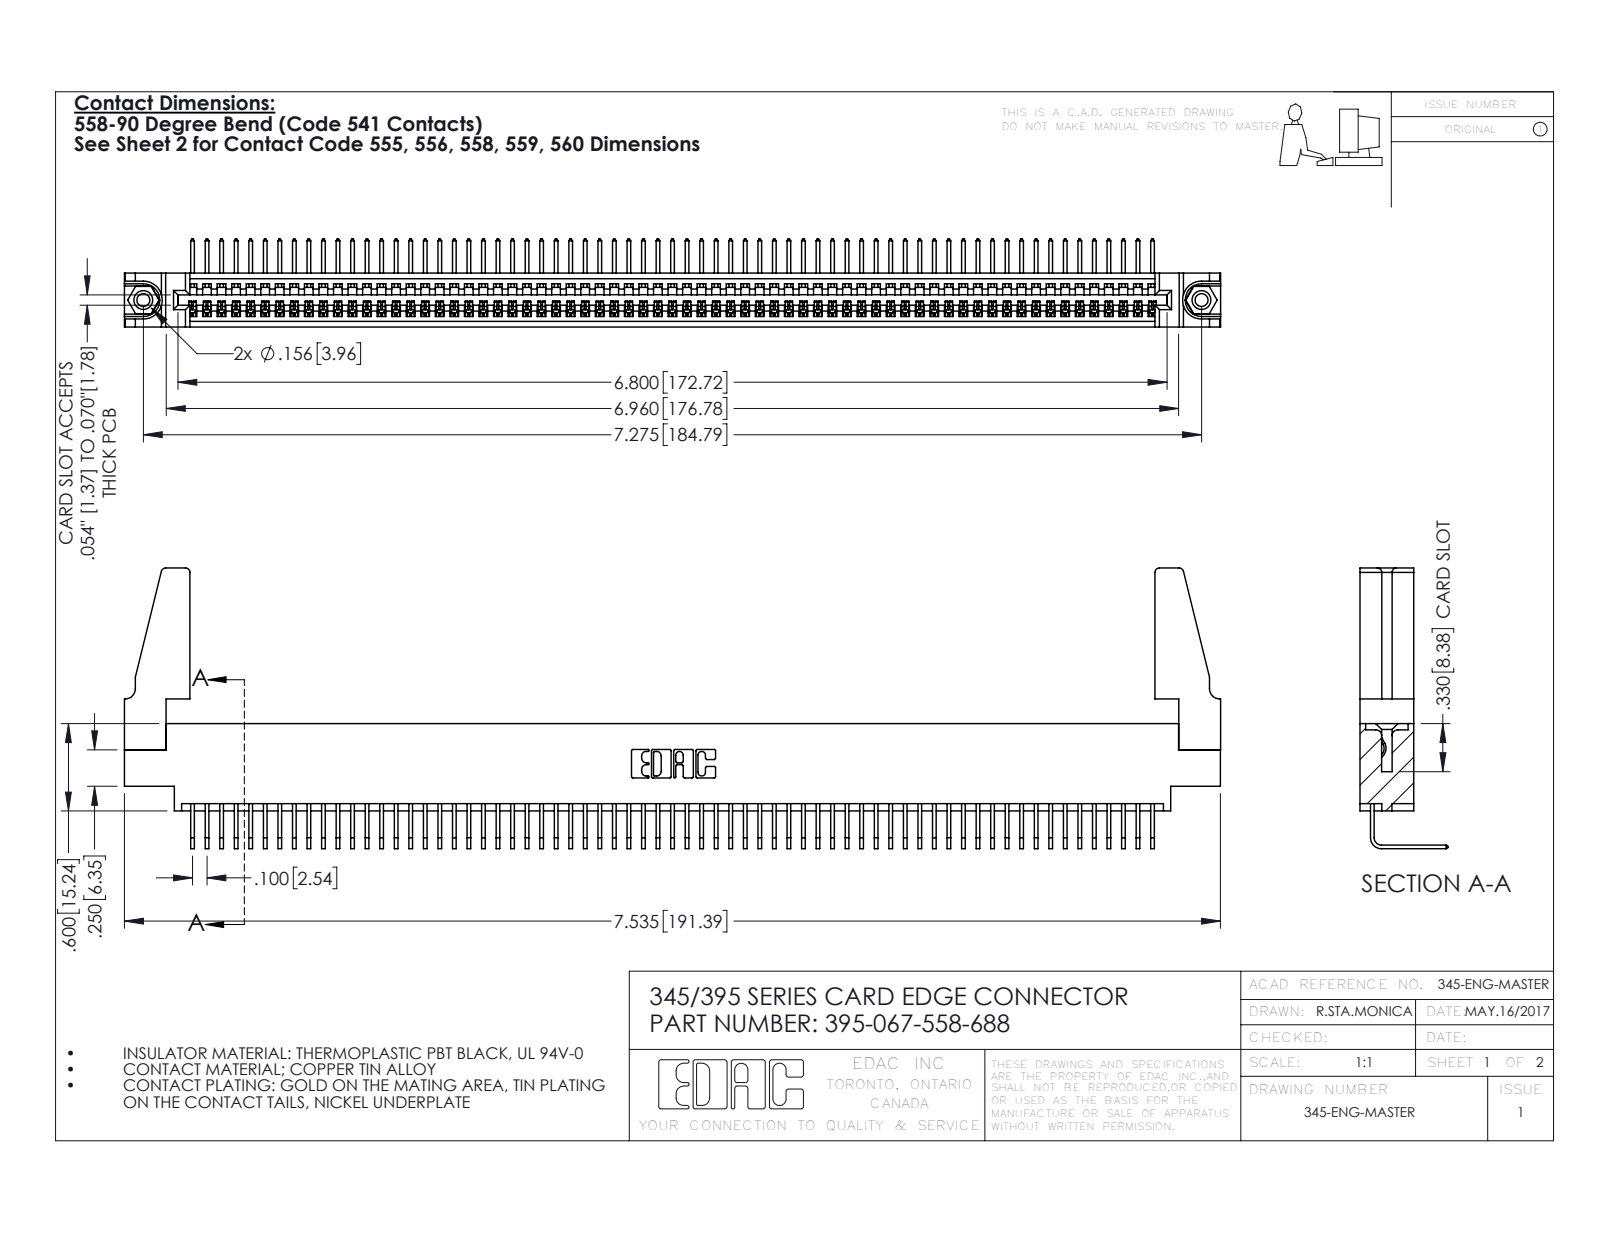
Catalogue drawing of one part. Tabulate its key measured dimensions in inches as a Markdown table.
| quantity | value |
| --- | --- |
| part name | 345-292-001_558 Tail - 2; 345 Part_0.170 Offset - 0.156 Dia-TH; 345-220-078_345-220-088; 345-250-001_345-250-001-102 (+1 more) |
| STEP written by | SolidWorks 2016 (CONFIG_CONTROL_DESIGN) |
| units | inches |
| bodies | 72 solids, 4274 faces (2970 planar, 1288 cylindrical, 16 other) |
| overall size | 7.536 × 1.929 × 0.605 |
| volume | 1.327 in³ |
| surface area | 45.7 in² |
| round holes (diameter × count) | 0.089 × 2, 0.125 × 2, 0.156 × 2, 0.064 × 1 |
| round bosses / shafts (diameter × count) | 0.155 × 2 |
| partial cylindrical surfaces (radius × count) | 0.006 × 134, 0.01 × 22, 0.03 × 8, 0.007 × 6, 0.031 × 6, 0.026 × 3, 0.031 × 2, 0.04 × 2 |
| main face-to-face distances | 0.072, 0.298, 0.37, 0.098, 0.272, 0.025, 0.2, 0.225, 0.175, 0.149 |
| hole center spacings | 0.27, 7.039, 7.275 |
